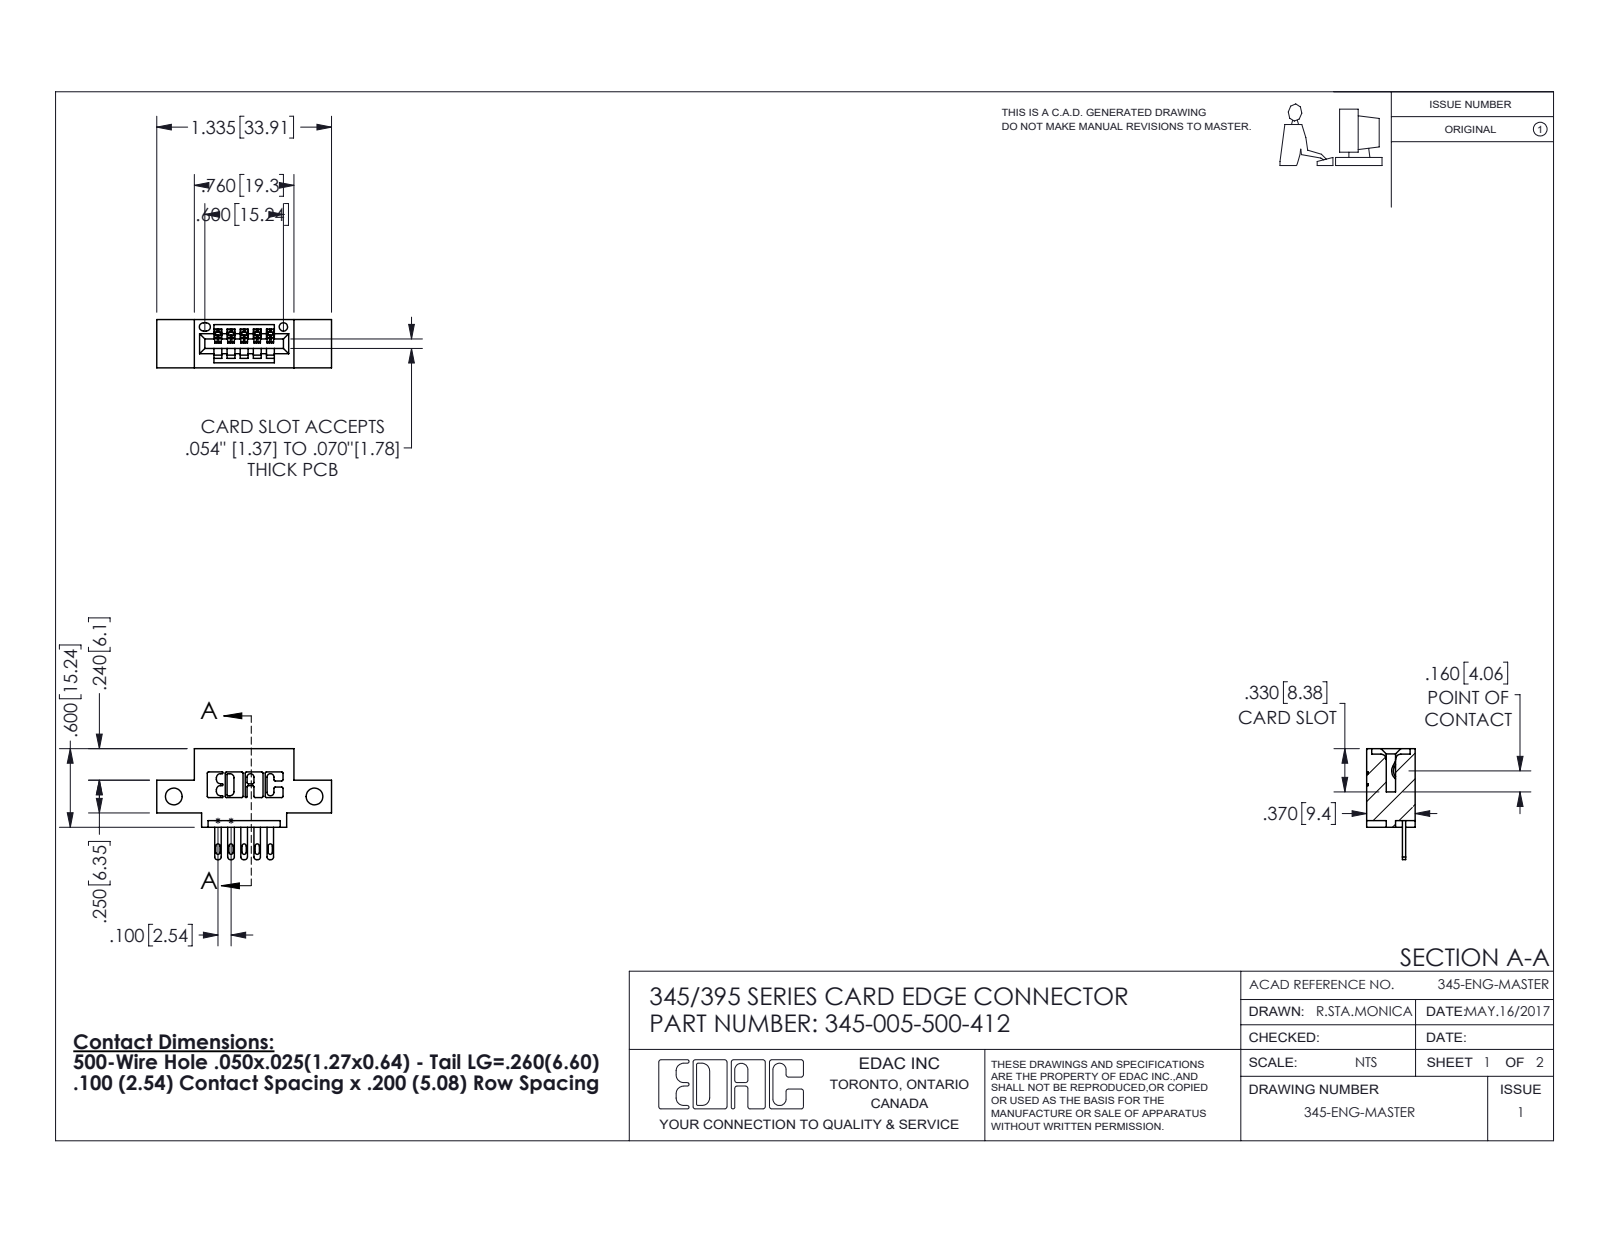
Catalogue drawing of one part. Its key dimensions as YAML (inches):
part_name: "345-005-500-412; 345-292-001_345-293-100; 345 Part_0.110 Offset - Side Mount"
step_written_by: "SolidWorks 2016 (CONFIG_CONTROL_DESIGN)"
units: inches
bodies: {solids: 6, faces: 400, planar: 254, cylindrical: 146, other: 0}
overall_size: [1.335, 0.847, 0.37]
volume: 0.168
surface_area: 4.83
round_holes:
  - {diameter: 0.128, count: 2}
  - {diameter: 0.064, count: 1}
partial_cylinders:
  - {radius: 0.01, count: 22}
  - {radius: 0.006, count: 10}
  - {radius: 0.016, count: 10}
  - {radius: 0.02, count: 10}
  - {radius: 0.007, count: 6}
  - {radius: 0.031, count: 6}
  - {radius: 0.026, count: 3}
  - {radius: 0.031, count: 2}
face_to_face_distances: [0.2, 0.37, 0.072, 0.298, 0.1, 0.25, 0.025, 0.098, 0.272, 0.06]
hole_center_spacings: [1.075]
